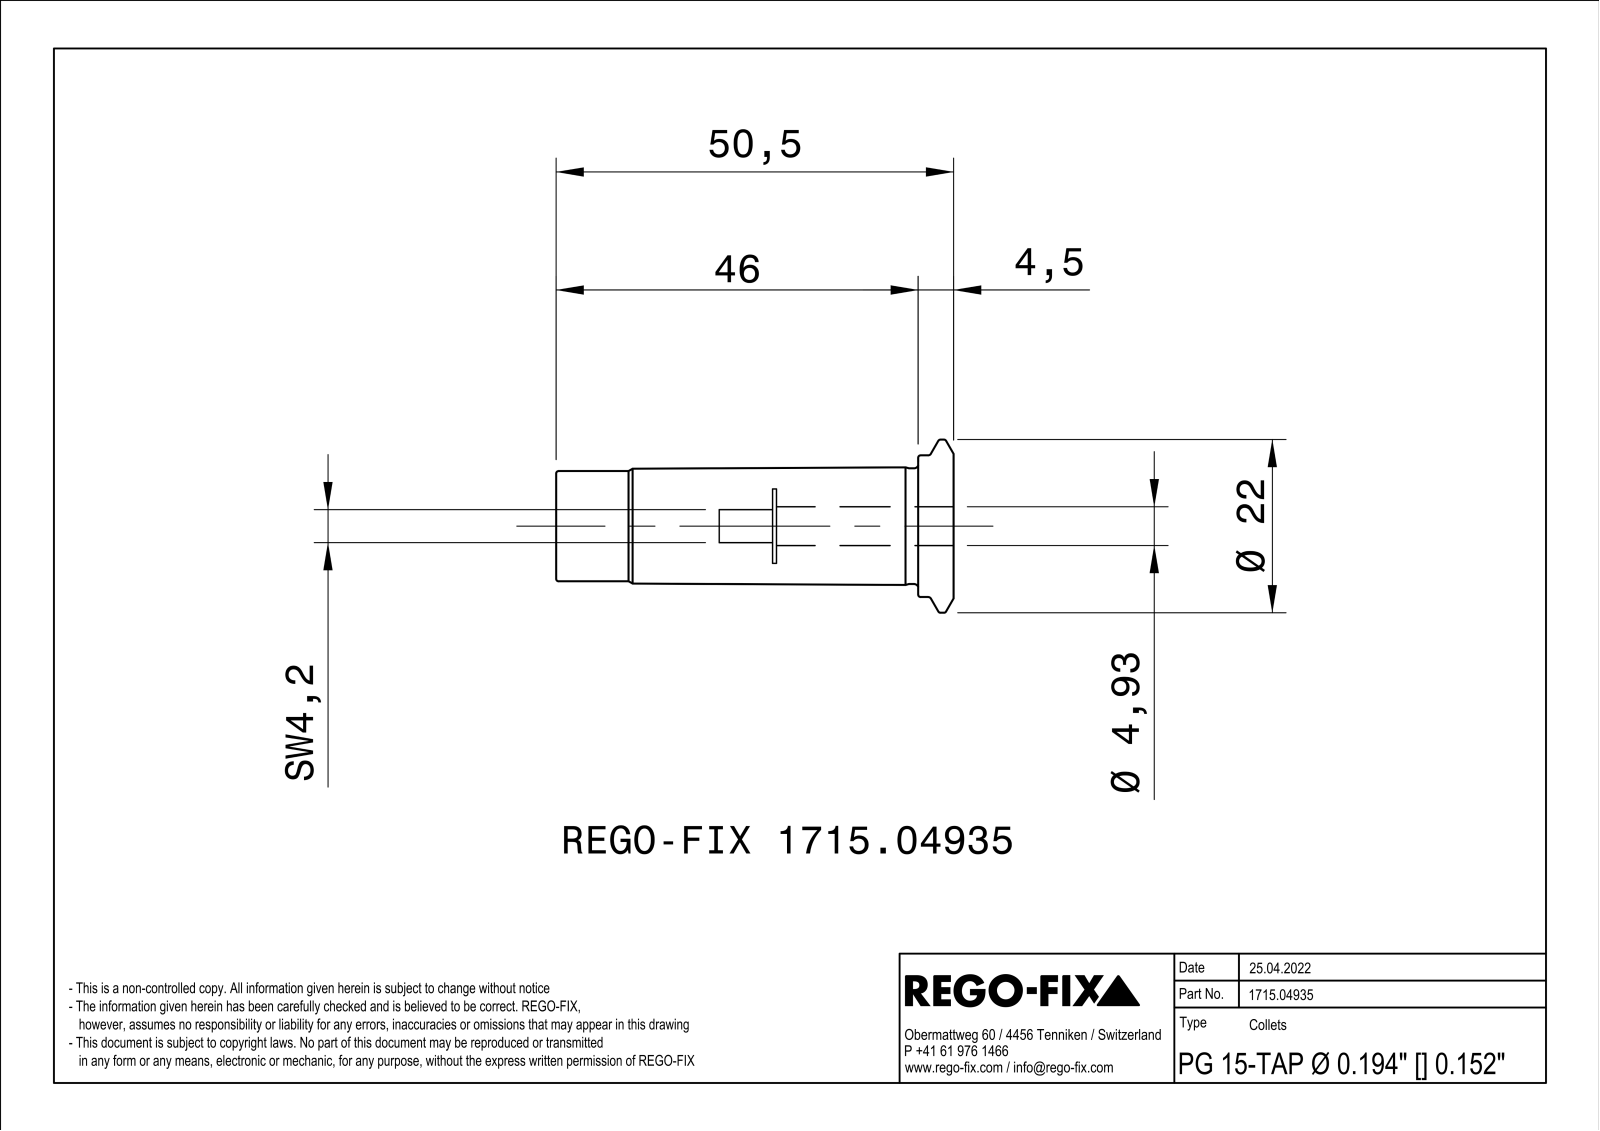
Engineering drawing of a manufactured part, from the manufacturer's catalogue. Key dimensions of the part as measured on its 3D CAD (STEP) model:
Part name (STEP PRODUCT): NOCUT
STEP written by: SIEMENS PLM Software Solid Edge ST10 (AUTOMOTIVE_DESIGN)
Units: millimetres
Bodies: 1 solid, 104 faces (25 planar, 28 cylindrical, 51 other)
Overall size (bounding box): 50.5 × 22 × 21.99
Volume: 6 941 mm³ · Surface area: 6 069 mm²
Round holes (diameter × count): ⌀4.93 ×1, ⌀6.92 ×1, ⌀7 ×1, ⌀8.4 ×1, ⌀11.1 ×1
Round bosses / shafts (diameter × count): ⌀22 ×1, ⌀18 ×1, ⌀14.7 ×1, ⌀14 ×1, ⌀11 ×1, ⌀10.9 ×1, ⌀10.5 ×1, ⌀10.2 ×1
Main face-to-face distances: 1, 50.5, 4.1, 22.5, 28, 23, 0.5, 27.5, 7, 21
